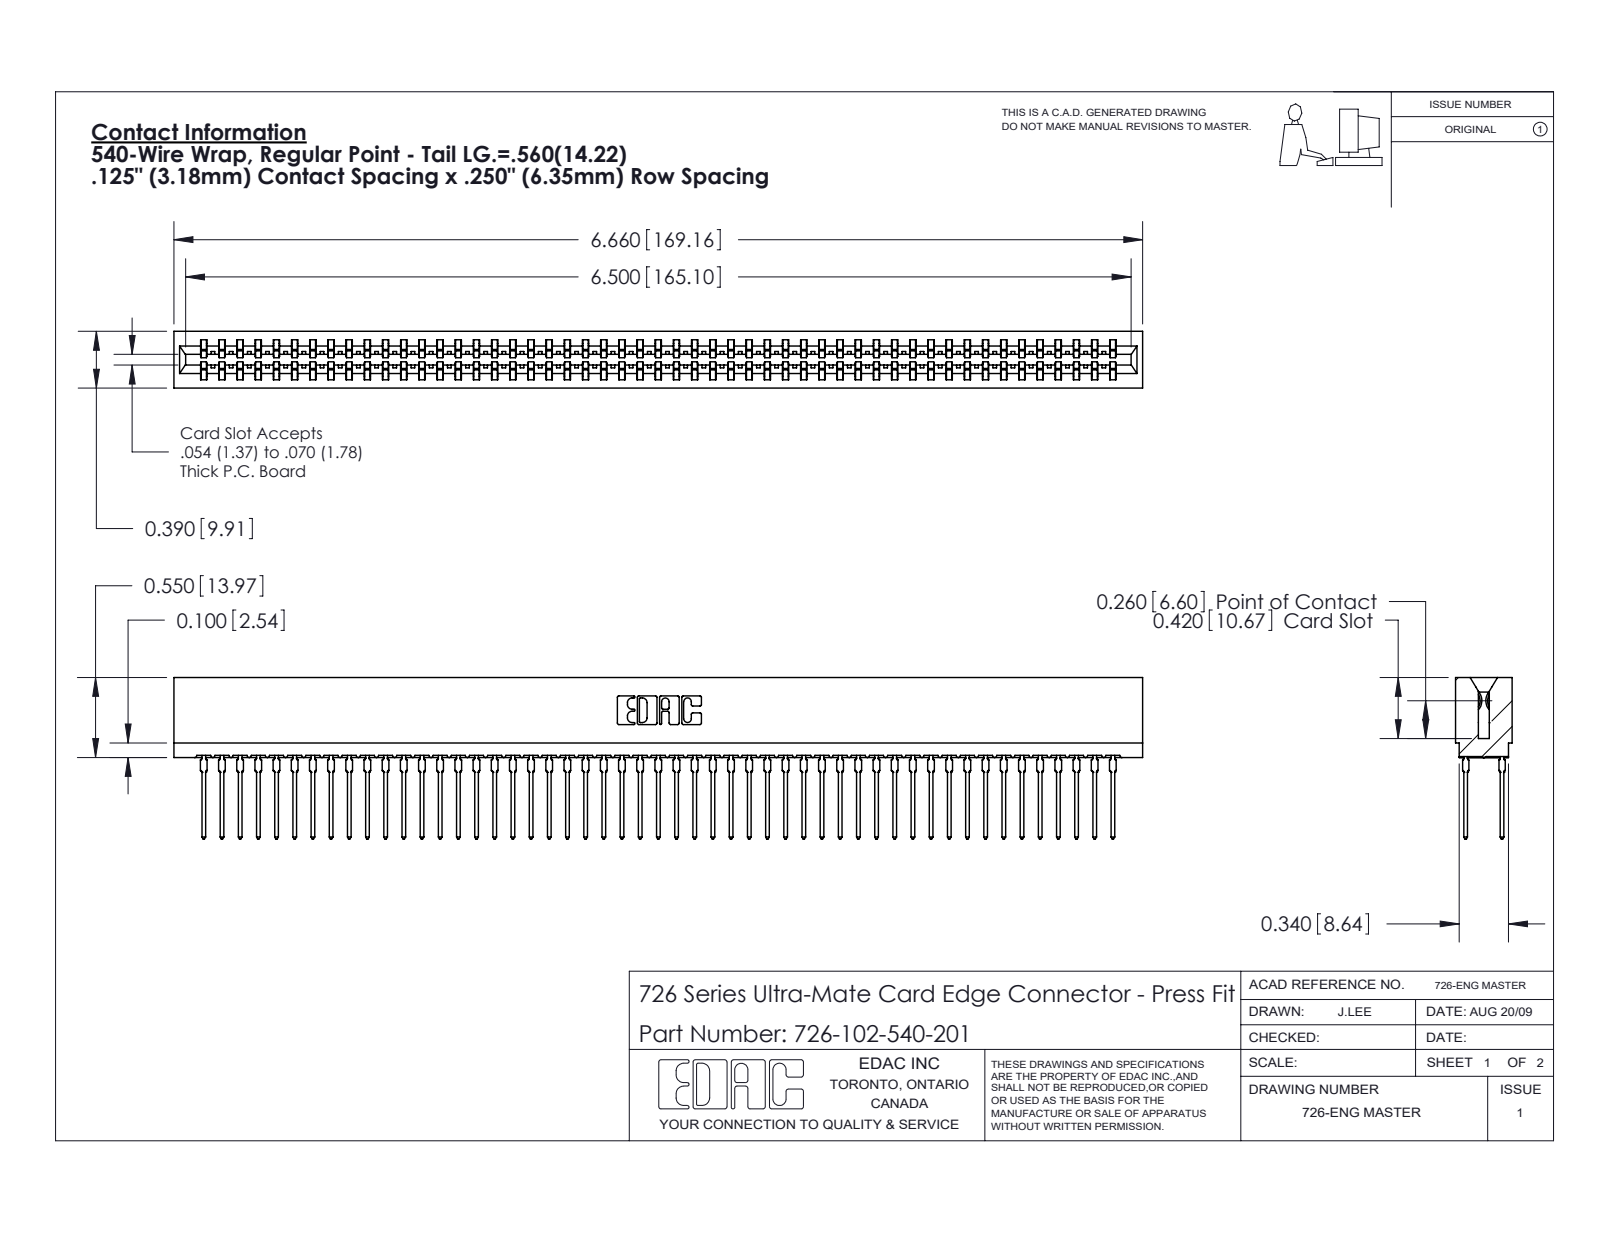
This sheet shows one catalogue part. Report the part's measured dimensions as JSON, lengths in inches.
{"part_name": "746-292-001_540; 726-102-540-201; 726 Part_.515 Slot Depth - 01", "step_written_by": "SolidWorks 2020 (CONFIG_CONTROL_DESIGN)", "units": "inches", "bodies": {"solids": 103, "faces": 9226, "planar": 4747, "cylindrical": 1827, "other": 2652}, "overall_size": [6.66, 1.109, 0.39], "volume_in3": 0.967, "surface_area_in2": 43.35, "partial_cylinders_radius": [[0.021, 204], [0.015, 52], [0.01, 22], [0.005, 8], [0.011, 8], [0.007, 6], [0.031, 6], [0.026, 3]], "face_to_face_distances": [0.057, 0.333, 0.025, 0.307, 0.25, 0.39, 0.275, 0.083, 0.365, 0.032]}
